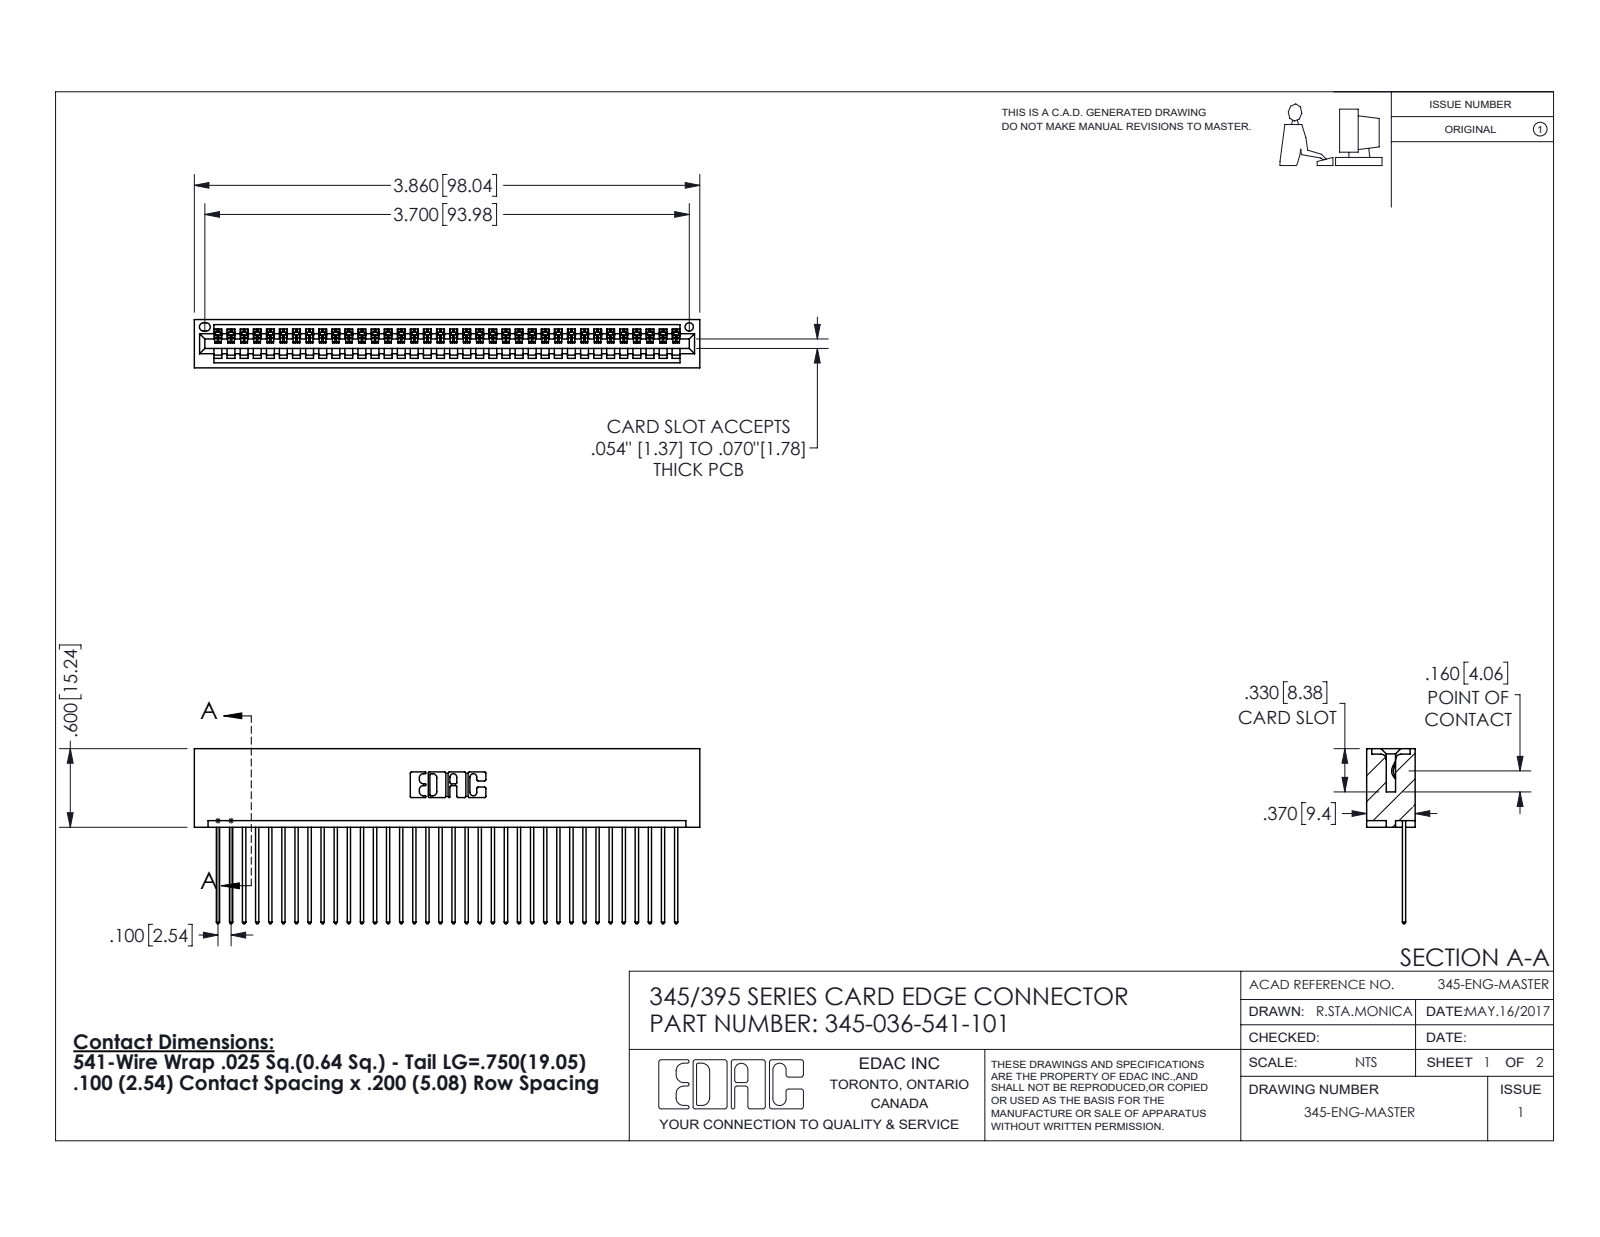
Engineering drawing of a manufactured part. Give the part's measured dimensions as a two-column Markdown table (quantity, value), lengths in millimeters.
| quantity | value |
| --- | --- |
| part name | 345-036-541-101; 345 Part_No Mounting Lugs; 345-292-001_345-293-141 |
| STEP written by | SolidWorks 2016 (CONFIG_CONTROL_DESIGN) |
| units | millimeters |
| bodies | 37 solids, 2206 faces (1516 planar, 690 cylindrical, 0 other) |
| overall size | 98 × 34 × 9.4 |
| volume | 9 960 mm³ |
| surface area | 14 050 mm² |
| round holes (diameter × count) | 1.6 × 1 |
| partial cylindrical surfaces (radius × count) | 0.2 × 72, 0.3 × 72, 0.3 × 22, 0.2 × 6, 0.8 × 6, 0.7 × 3, 0.8 × 2, 1 × 2 |
| main face-to-face distances | 1.8, 7.6, 2.5, 6.9, 0.6, 9.4, 5.1, 5.7, 3.8, 1.8 |
